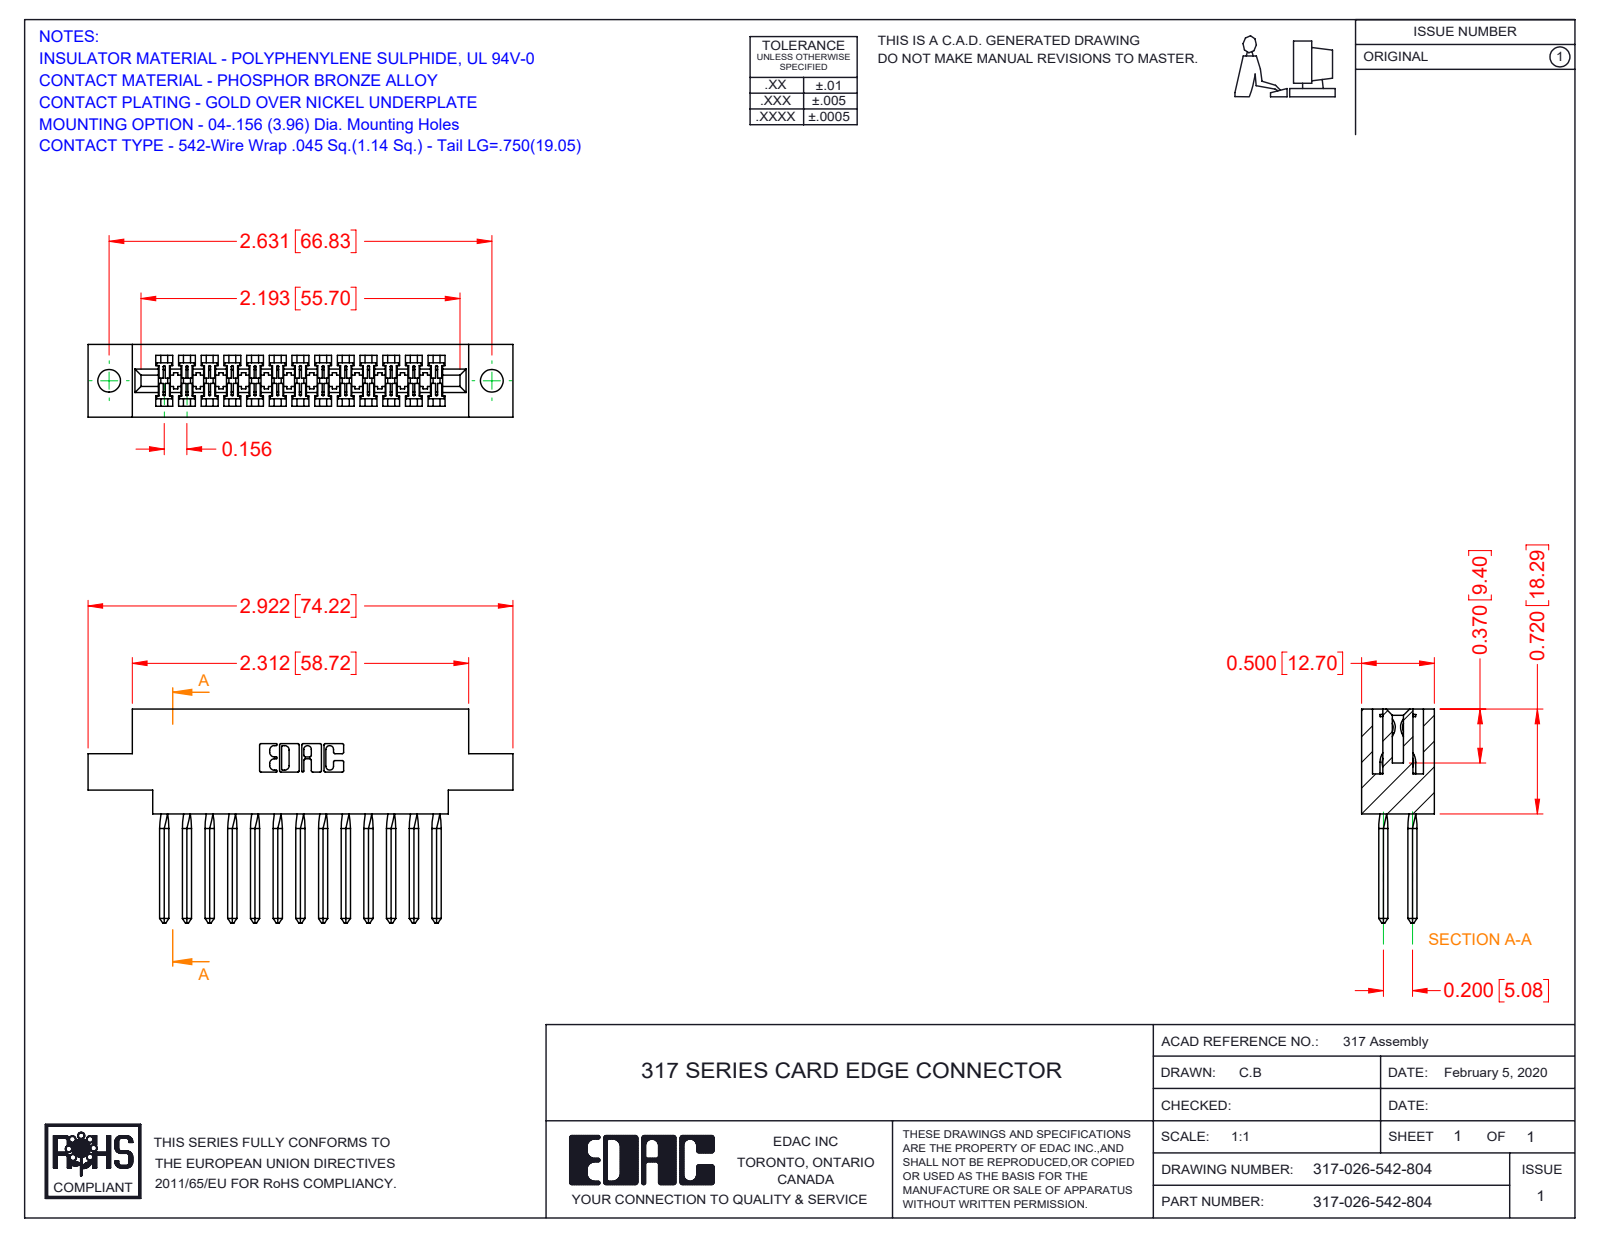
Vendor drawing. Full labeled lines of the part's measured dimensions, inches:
Part name (STEP PRODUCT): 317-290-003_542; 317 Part_.156 Dia - TH; 317-026-542-804
STEP written by: SolidWorks 2016 (CONFIG_CONTROL_DESIGN)
Units: inches
Bodies: 27 solids, 1584 faces (1254 planar, 226 cylindrical, 104 other)
Overall size (bounding box): 2.922 × 1.47 × 0.5
Volume: 0.68 in³ · Surface area: 22.3 in²
Round holes (diameter × count): ⌀0.156 ×2
Partial cylindrical surfaces — rounded edges, fillets, slot ends (radius × count): R0.006 ×52, R0.01 ×22, R0.007 ×6, R0.031 ×6, R0.026 ×3, R0.074 ×2, R0.089 ×2, R0.1 ×2
Main face-to-face distances: 0.5, 0.075, 0.425, 0.11, 0.35, 0.22, 0.116, 0.2, 0.136, 0.72
Hole centre spacings: 2.631
